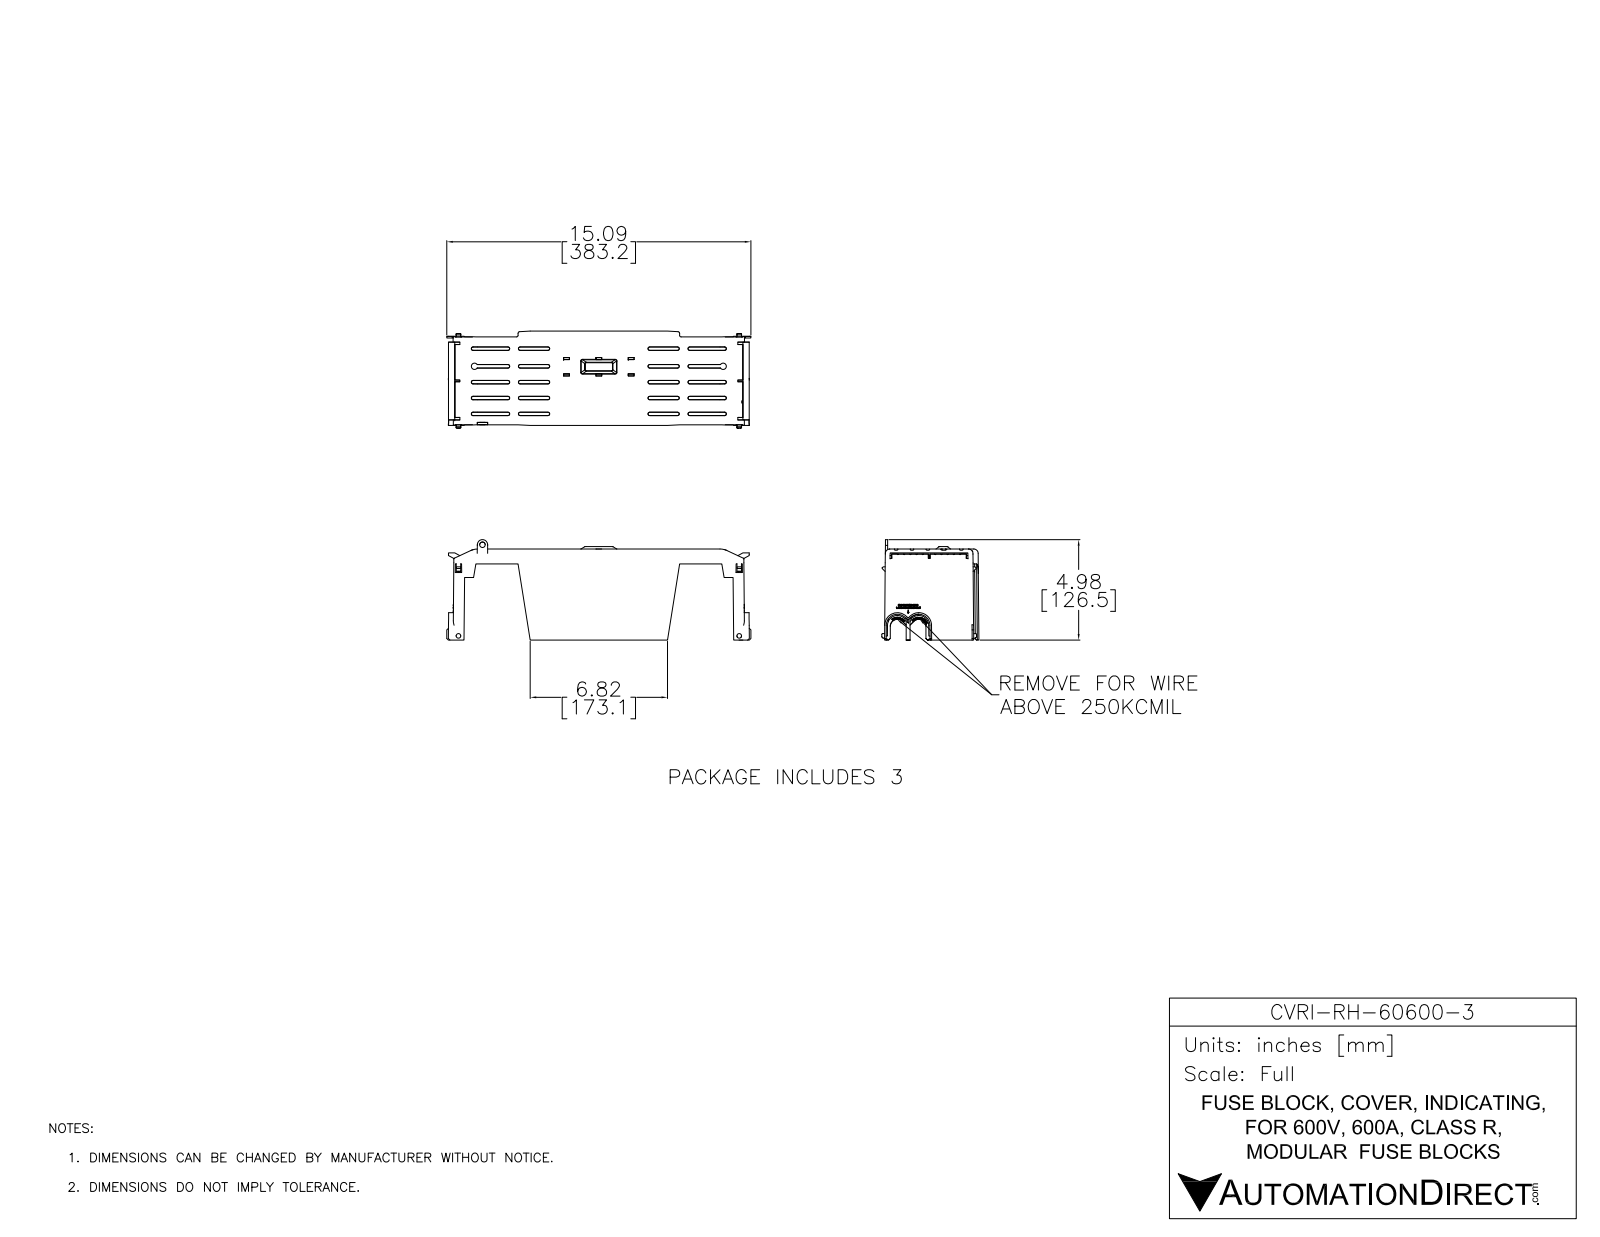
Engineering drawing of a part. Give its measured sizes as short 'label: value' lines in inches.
name: CVRI-RH-60600-3
written by: SolidWorks 2017 (AUTOMOTIVE_DESIGN)
unit: in
bodies: 1 solid, 2399 faces (1630 planar, 123 cylindrical, 646 other)
size: 15.085 × 4.983 × 4.817
volume: 15.84 in³; area: 413.6 in²
holes: 1× ⌀0.276
bosses: 2× ⌀0.228
rounds: 18× R0.039, 8× R0.118, 7× R0.138, 7× R0.217, 4× R0.079, 4× R0.354, 4× R0.492, 4× R0.551
face distances: 0.079, 0.256, 0.177, 0.795, 0.197, 0.335, 0.803, 0.118, 0.402, 1.598
